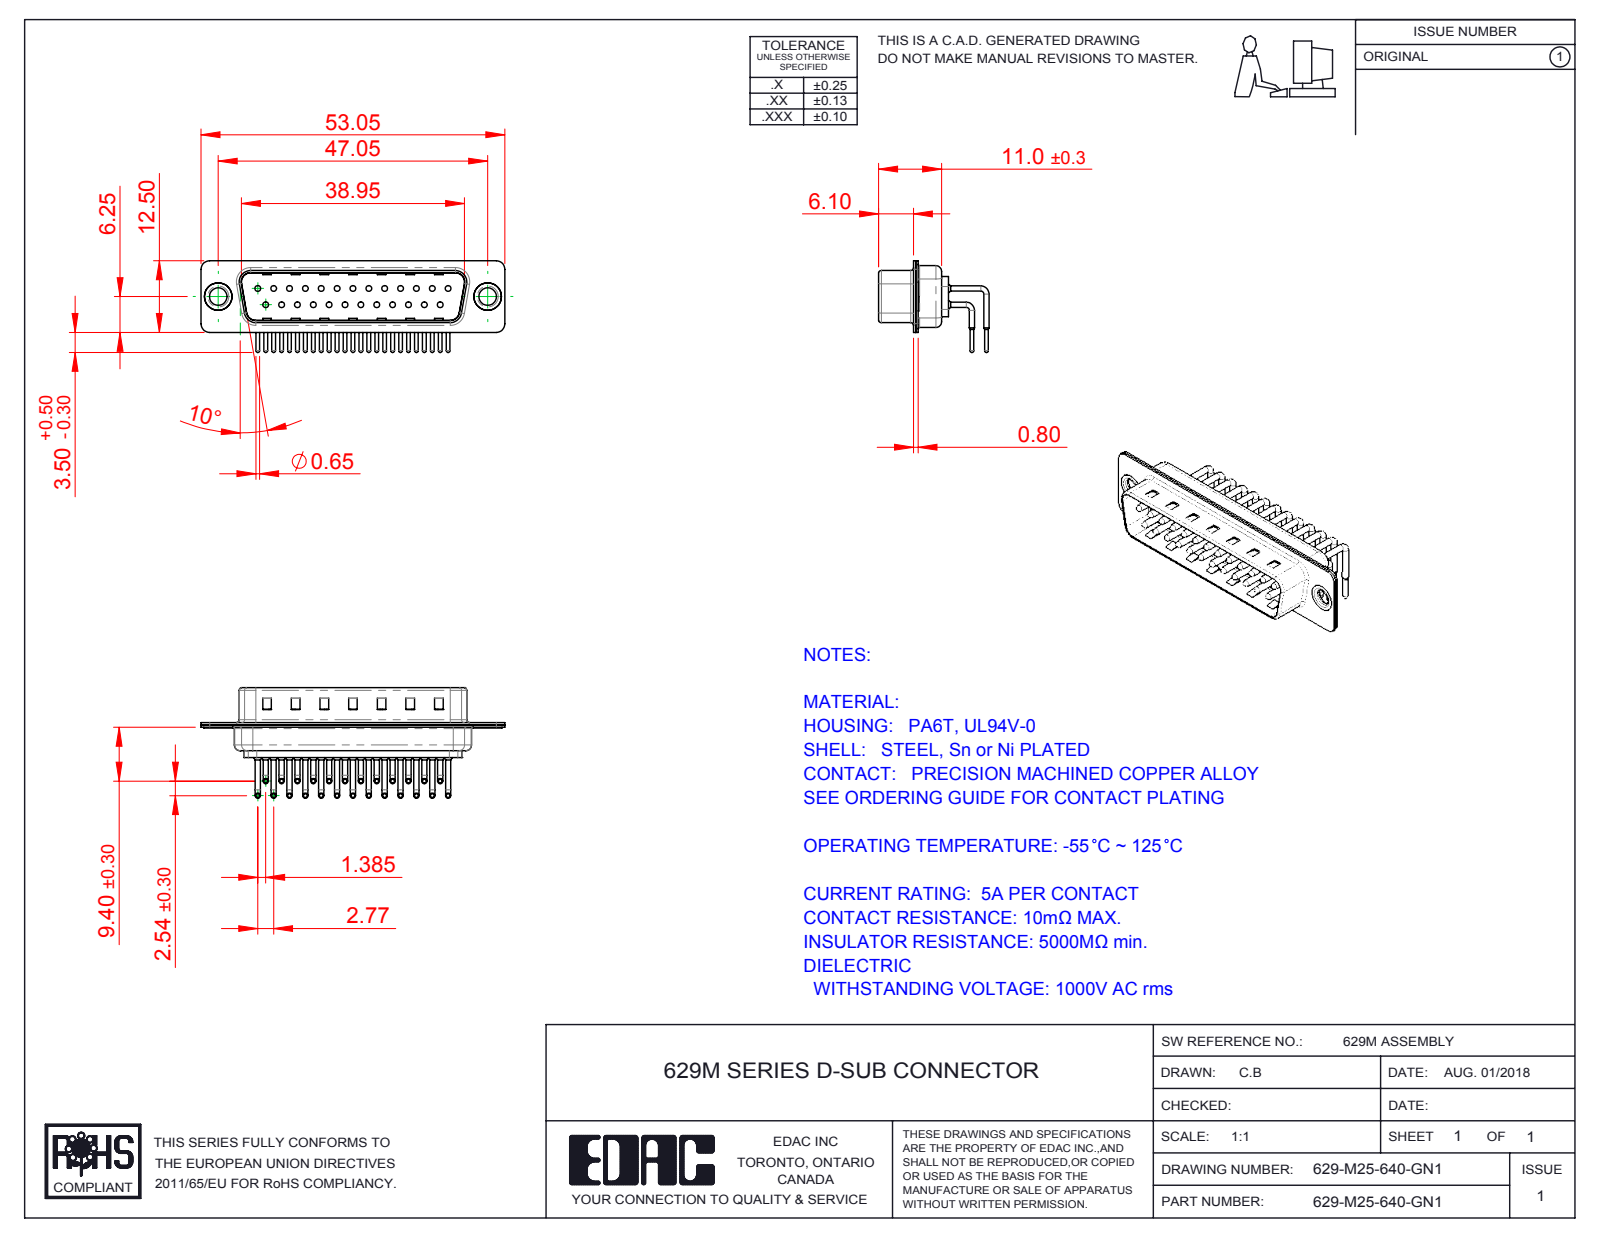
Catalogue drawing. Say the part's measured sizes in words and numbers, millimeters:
The part is named "629M Thru Hole Rivet; 629M Shell Front_25 Contacts; 629M Contact Row 1; 629M Contact Row 2 (+3 more)". Its 3-D file was written by "SolidWorks 2016 (CONFIG_CONTROL_DESIGN)". It is 30 solids with 3100 faces: 1771 planar, 1021 cylindrical and 308 other. Overall it measures 53.05 by 19.29 by 16 millimeters. Its volume is 2 832 cubic millimeters and its surface area 7 610 square millimeters. Round holes: 25 of diameter 1, 25 of diameter 1.7, 25 of diameter 2, 2 of diameter 3.05, 2 of diameter 4, 2 of diameter 4.8. Round bosses or shafts: 50 of diameter 0.9, 25 of diameter 1.5, 25 of diameter 0.65, 2 of diameter 5, 2 of diameter 4.9, 2 of diameter 3.55. Partial cylindrical surfaces (rounded edges, fillets, slot ends): 25 of radius 1.01, 16 of radius 1.5, 12 of radius 2, 8 of radius 0.5, 8 of radius 1.6, 4 of radius 0.25, 4 of radius 0.6, 4 of radius 0.65. The main face-to-face distances are 0.4, 0.85, 9.55, 8.7, 1.25, 10.4, 1.5, 1.9, 0.35, 6.1. The hole center spacings are 3.16, 2.77, 5.54, 8.31, 11.08, 13.85, 5.04, 7.49.
